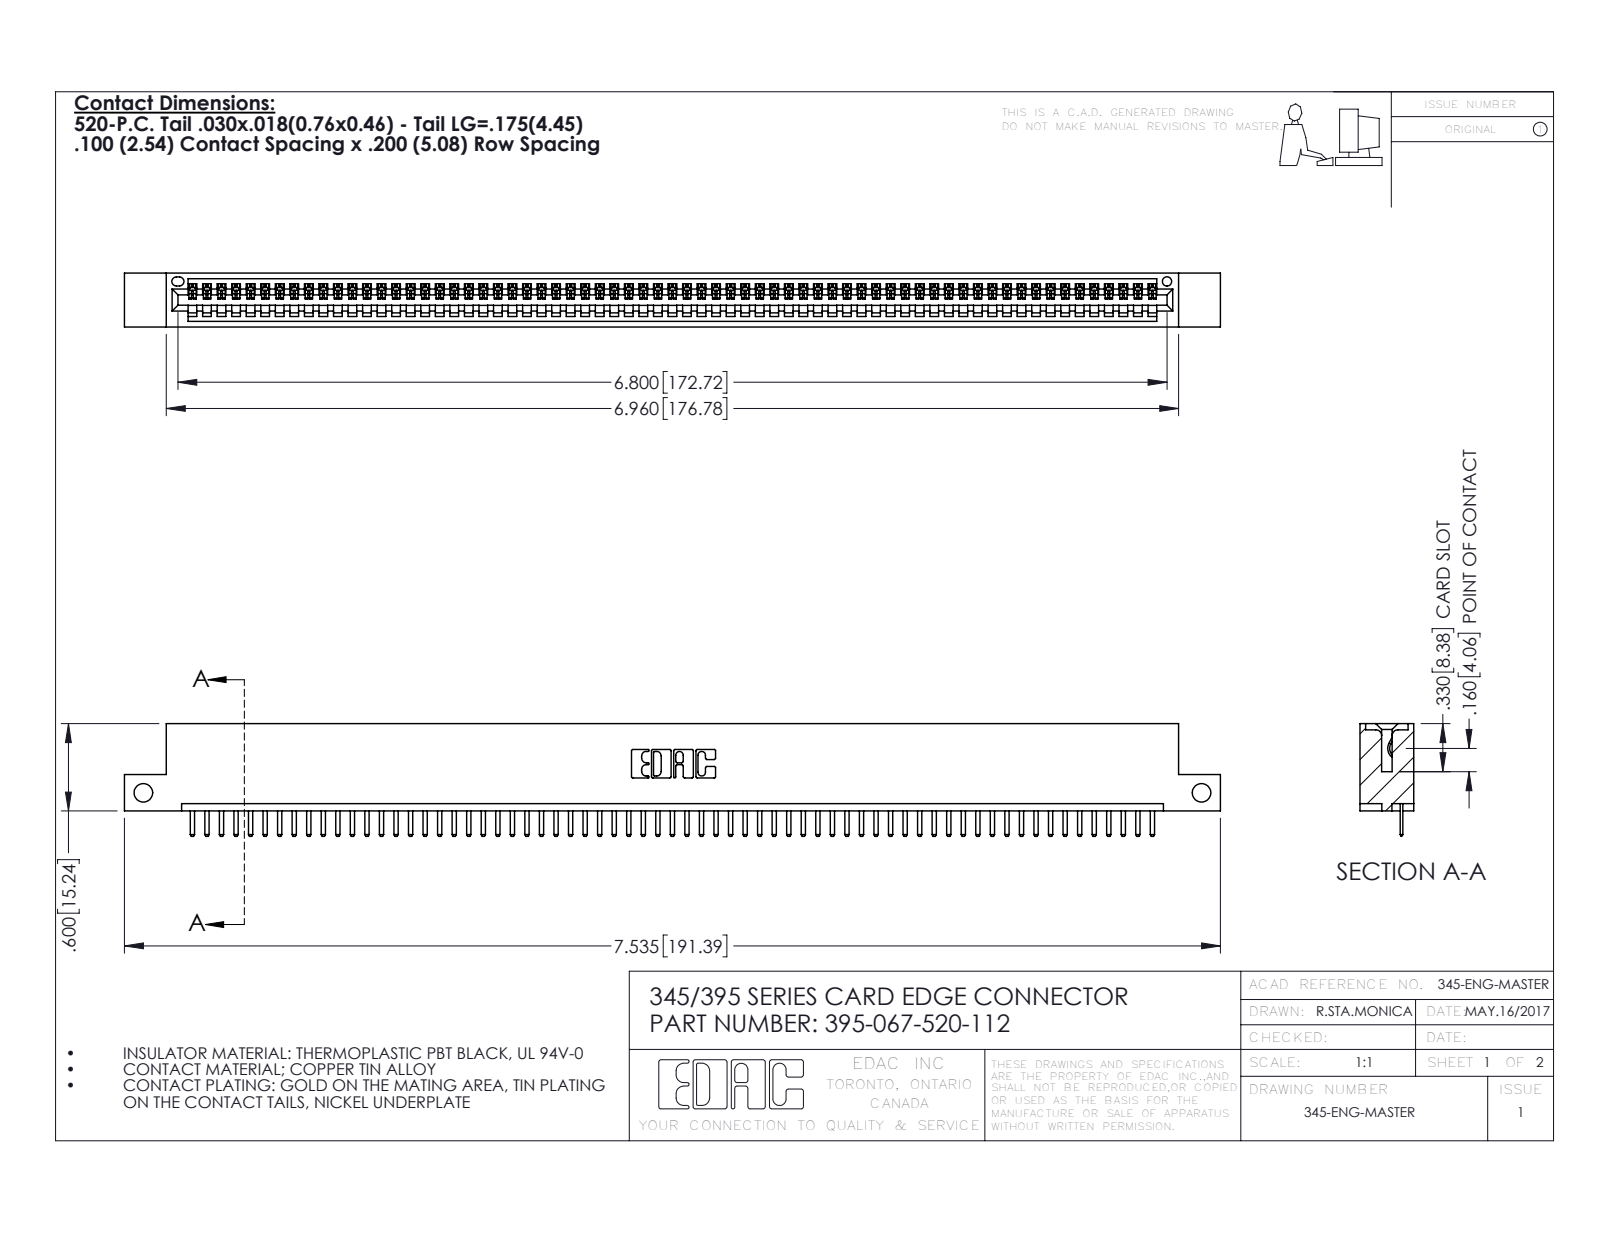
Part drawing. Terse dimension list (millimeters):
name: 345-292-001_345-293-120; 395-067-520-112; 345 Part_Flush Mounting Lugs - Side Mount
written by: SolidWorks 2016 (CONFIG_CONTROL_DESIGN)
unit: mm
bodies: 68 solids, 4280 faces (2894 planar, 1386 cylindrical, 0 other)
size: 191.4 × 19.7 × 9.4
volume: 18 110 mm³; area: 23 630 mm²
holes: 2× ⌀3.3, 1× ⌀1.6
rounds: 136× R0.3, 134× R0.2, 22× R0.3, 6× R0.2, 6× R0.8, 3× R0.7, 2× R0.8, 2× R1
face distances: 7.6, 1.8, 9.4, 5.1, 2.5, 6.9, 0.6, 5.7, 1.8, 3.8
hole spacings: 184.8
